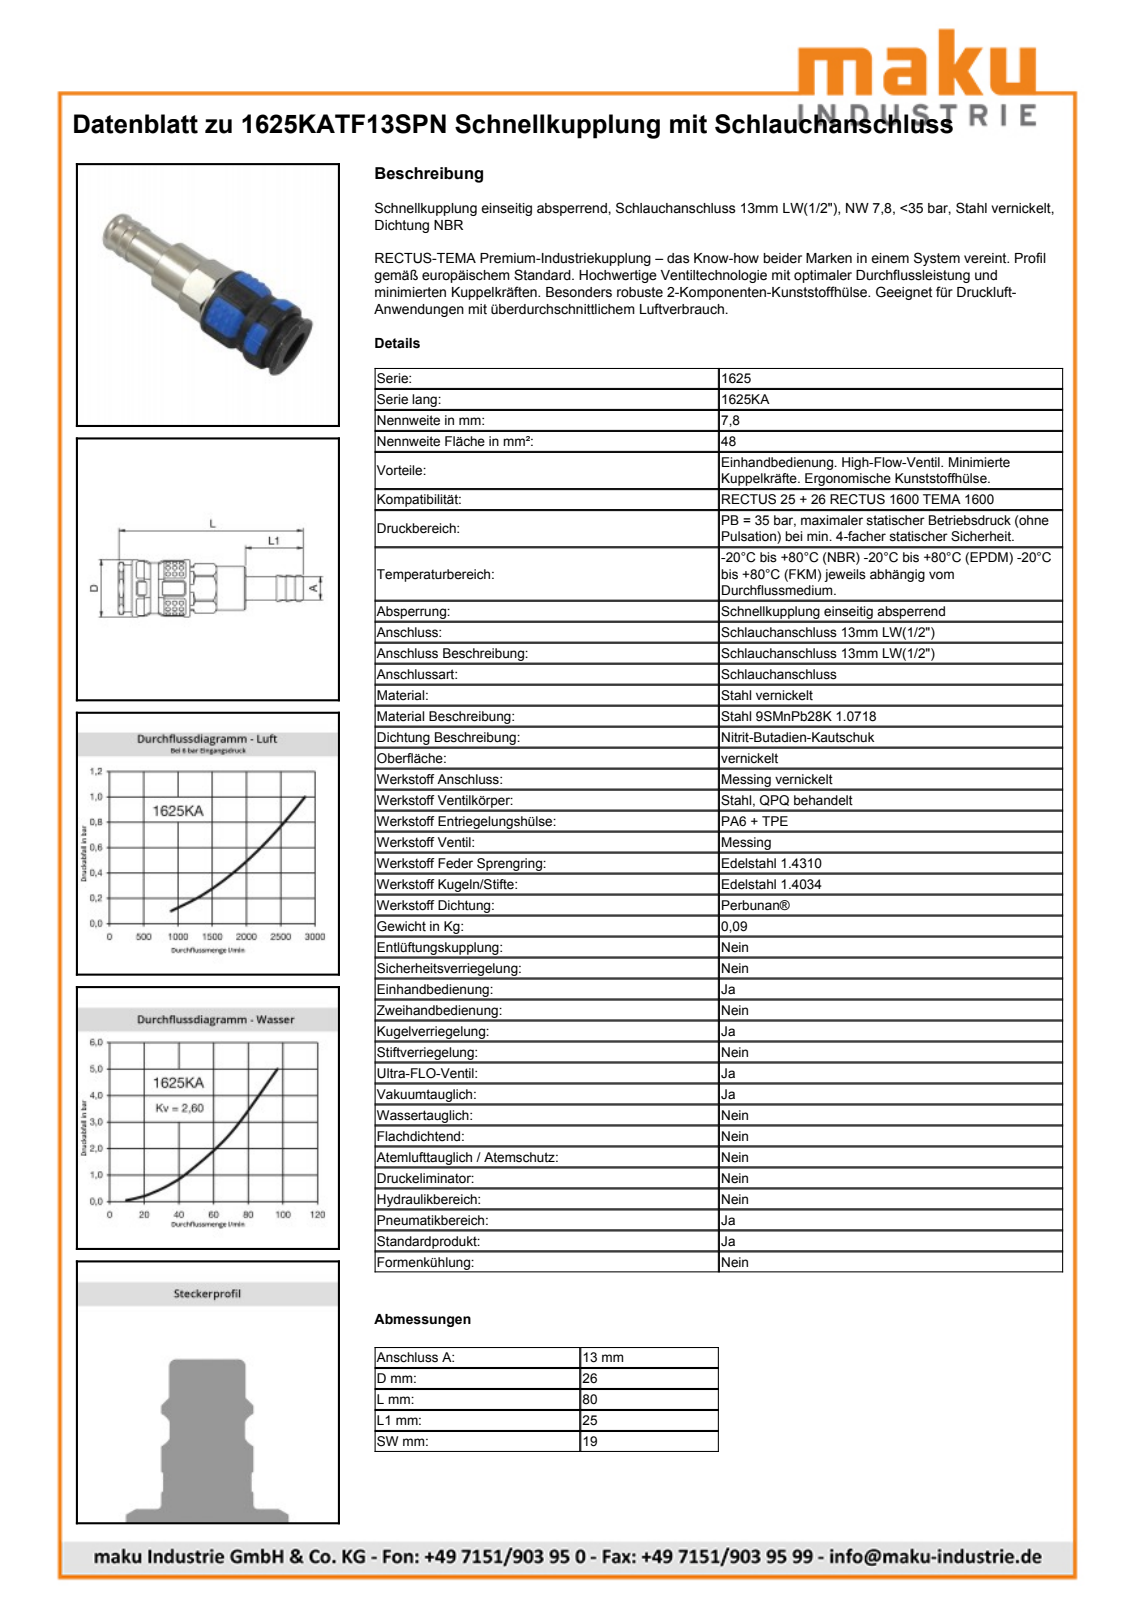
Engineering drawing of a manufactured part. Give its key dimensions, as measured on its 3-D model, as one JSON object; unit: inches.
{"part_name": "D105554", "step_written_by": "Autodesk Inventor 2011 (AUTOMOTIVE_DESIGN)", "units": "inches", "bodies": {"solids": 2, "faces": 986, "planar": 357, "cylindrical": 164, "other": 465}, "overall_size": [3.141, 0.984, 0.984], "volume_in3": 1.333, "surface_area_in2": 20.02, "round_holes": [[0.039, 4], [0.512, 1], [0.551, 1], [0.571, 1], [0.636, 1], [0.677, 1], [0.705, 1], [0.772, 1], [0.815, 1]], "round_bosses_or_shafts": [[0.984, 1], [0.866, 1], [0.799, 1], [0.74, 1], [0.693, 1], [0.669, 1], [0.618, 1], [0.569, 1]], "partial_cylinders_radius": [[0.016, 8], [0.38, 1], [0.421, 1], [0.441, 1], [0.443, 1], [0.453, 1], [0.472, 1], [0.484, 1]], "face_to_face_distances": [0.748, 3.141, 1.218, 1.924, 2.157, 0.939, 0.984, 0.996, 0.222, 1.935], "hole_center_spacings": [0.504]}
